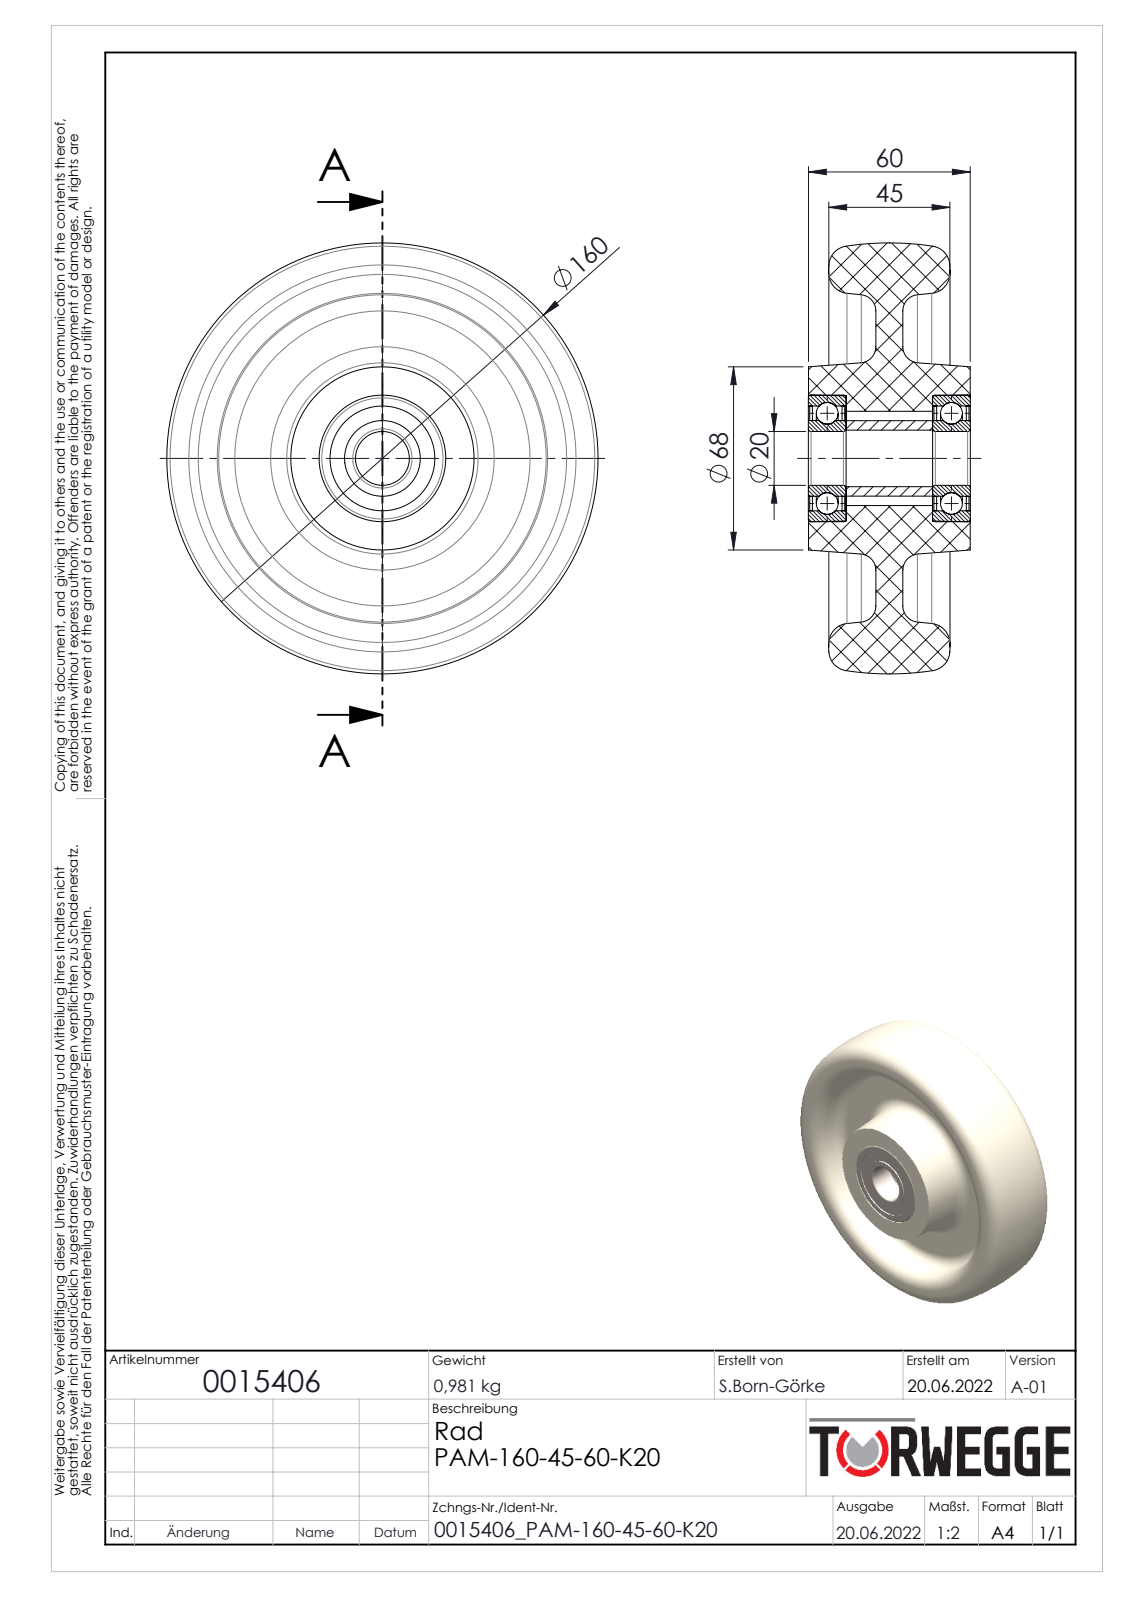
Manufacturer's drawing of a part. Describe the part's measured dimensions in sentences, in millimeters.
The part is named "0015406". Its 3-D file was written by "SolidWorks 2020 (AUTOMOTIVE_DESIGN)". It is 12 solids with 142 faces: 24 planar, 46 cylindrical and 72 other. Overall it measures 160 by 160 by 60.1 millimeters. Its volume is 624 928 cubic millimeters and its surface area 113 182 square millimeters. Round holes: 1 of diameter 20, 1 of diameter 21, 1 of diameter 28.1, 1 of diameter 35, 1 of diameter 38.9. Round bosses or shafts: 1 of diameter 47, 1 of diameter 28. The main face-to-face distances are 10, 25, 35, 46.1, 46.05, 14, 11, 0.5, 1.5, 12.5.
